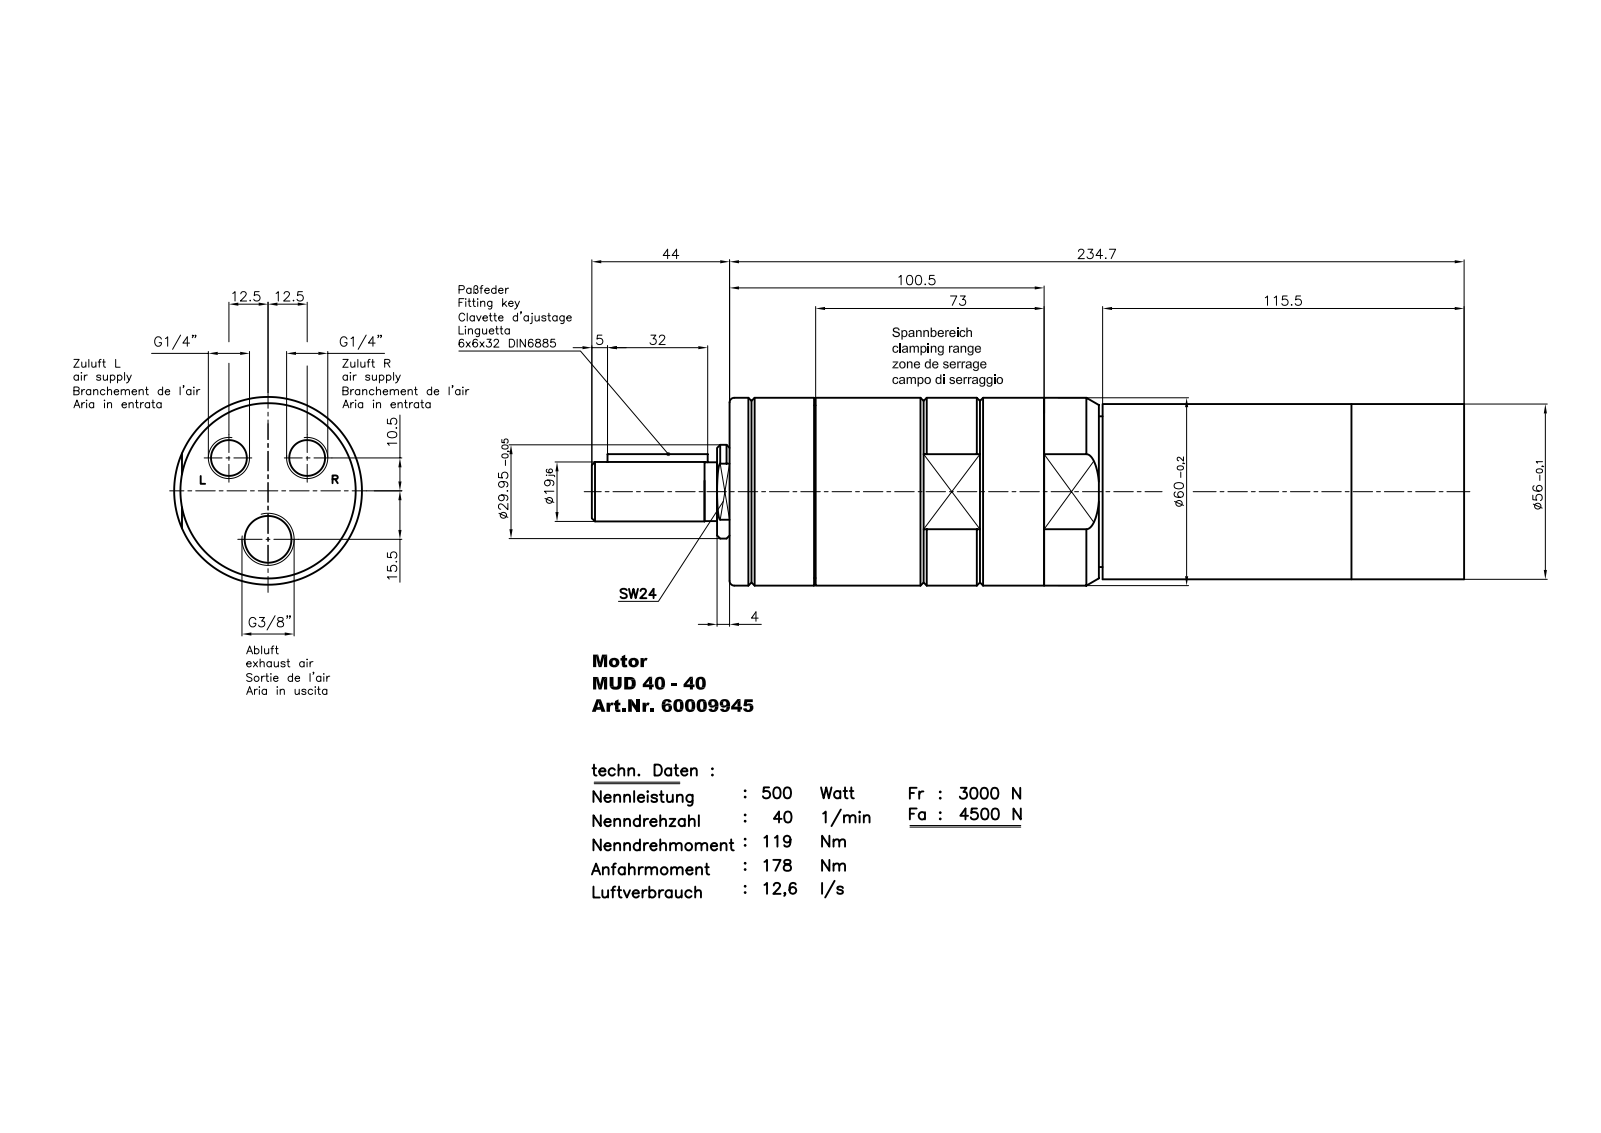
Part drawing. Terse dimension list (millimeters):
name: MUD 40-40_60009945
written by: Autodesk Inventor 2008 (CONFIG_CONTROL_DESIGN)
unit: mm
bodies: 1 solid, 109 faces (39 planar, 31 cylindrical, 39 other)
size: 278.7 × 60 × 60
volume: 622 864 mm³; area: 55 587 mm²
holes: 1× ⌀1.55, 1× ⌀4, 1× ⌀5.5, 1× ⌀35
bosses: 1× ⌀60, 1× ⌀57.48, 1× ⌀56, 1× ⌀53.06, 1× ⌀29.95, 1× ⌀19, 1× ⌀18.8, 1× ⌀5
rounds: 2× R3, 1× R11, 1× R23, 1× R26.64
face distances: 234.7, 219.86, 14.84, 54.99, 55.01, 4, 223.86, 238.7, 5.52, 1.52
